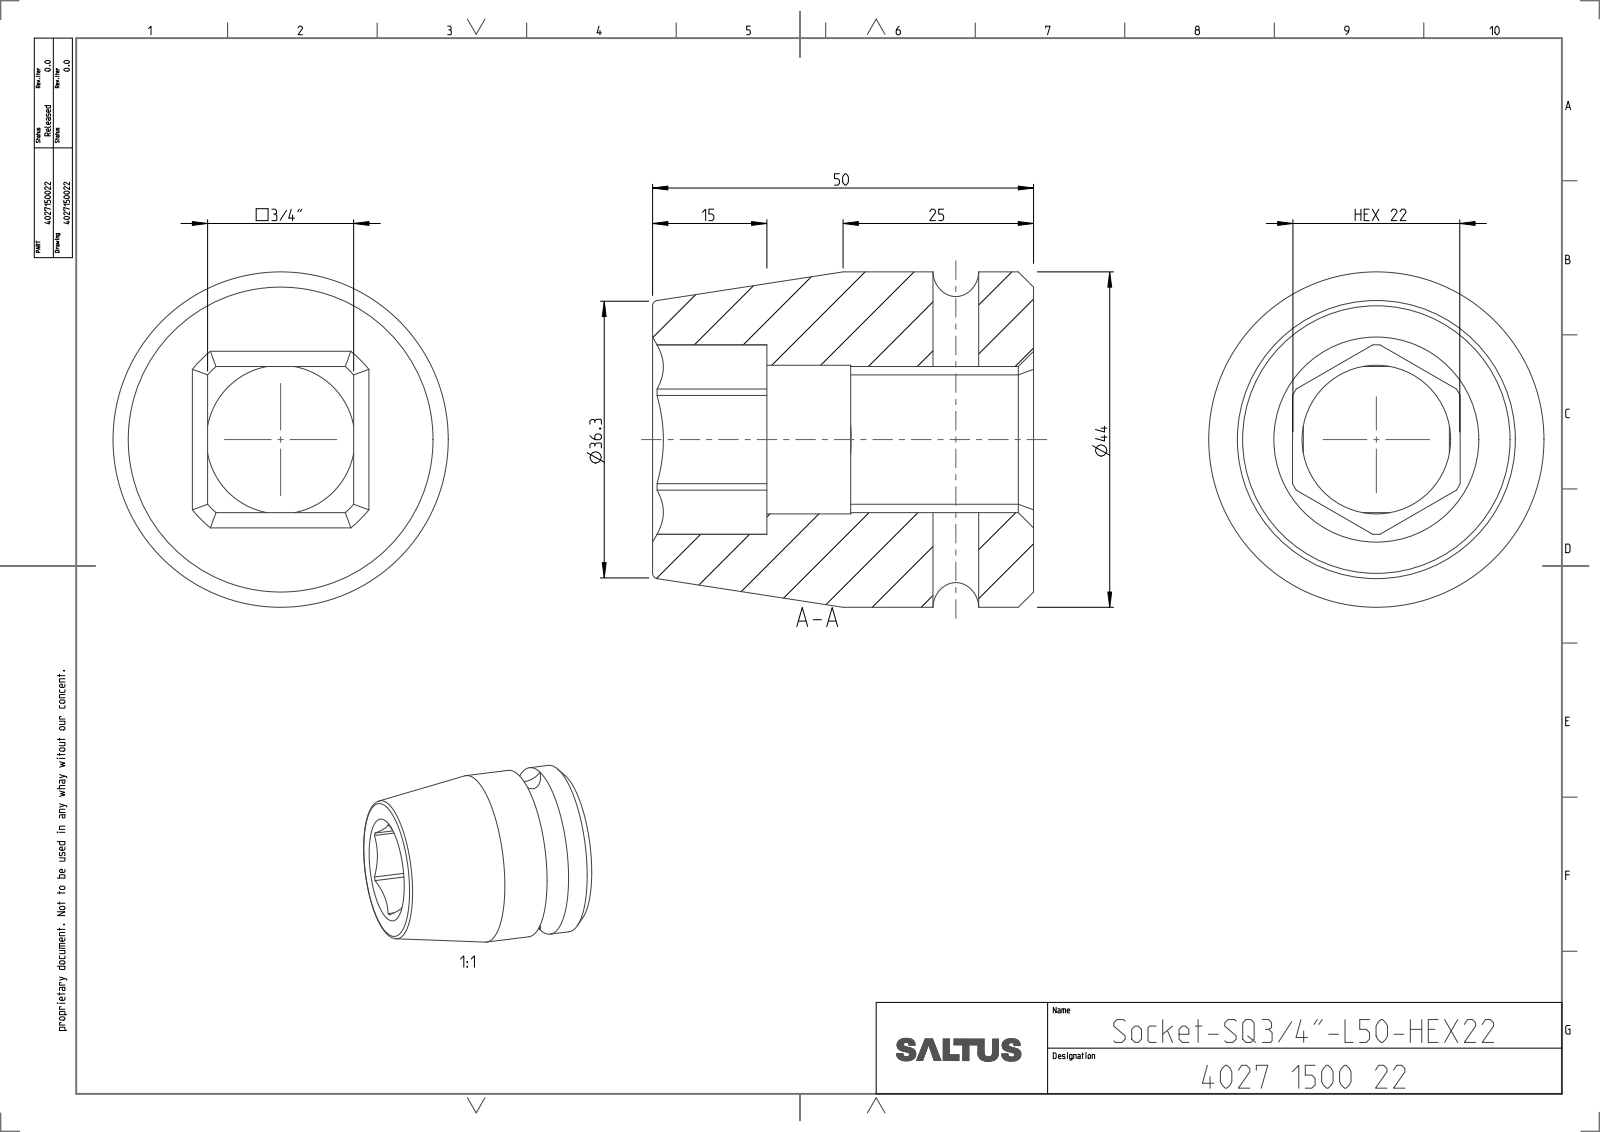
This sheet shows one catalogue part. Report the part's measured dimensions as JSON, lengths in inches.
{"part_name": "4027150022", "step_written_by": "CREO PARAMETRIC BY PTC INC, 2022414 (CONFIG_CONTROL_DESIGN)", "units": "inches", "bodies": {"solids": 1, "faces": 59, "planar": 21, "cylindrical": 20, "other": 18}, "overall_size": [1.969, 1.732, 1.732], "volume_in3": 2.961, "surface_area_in2": 19.35, "round_holes": [[0.236, 1], [0.768, 1]], "round_bosses_or_shafts": [[1.732, 1]], "partial_cylinders_radius": [[0.489, 1], [0.504, 1]], "face_to_face_distances": [0.755, 0.866, 1.969, 0.056, 0.811, 1.378, 0.591, 0.945, 0.433, 1.024]}
